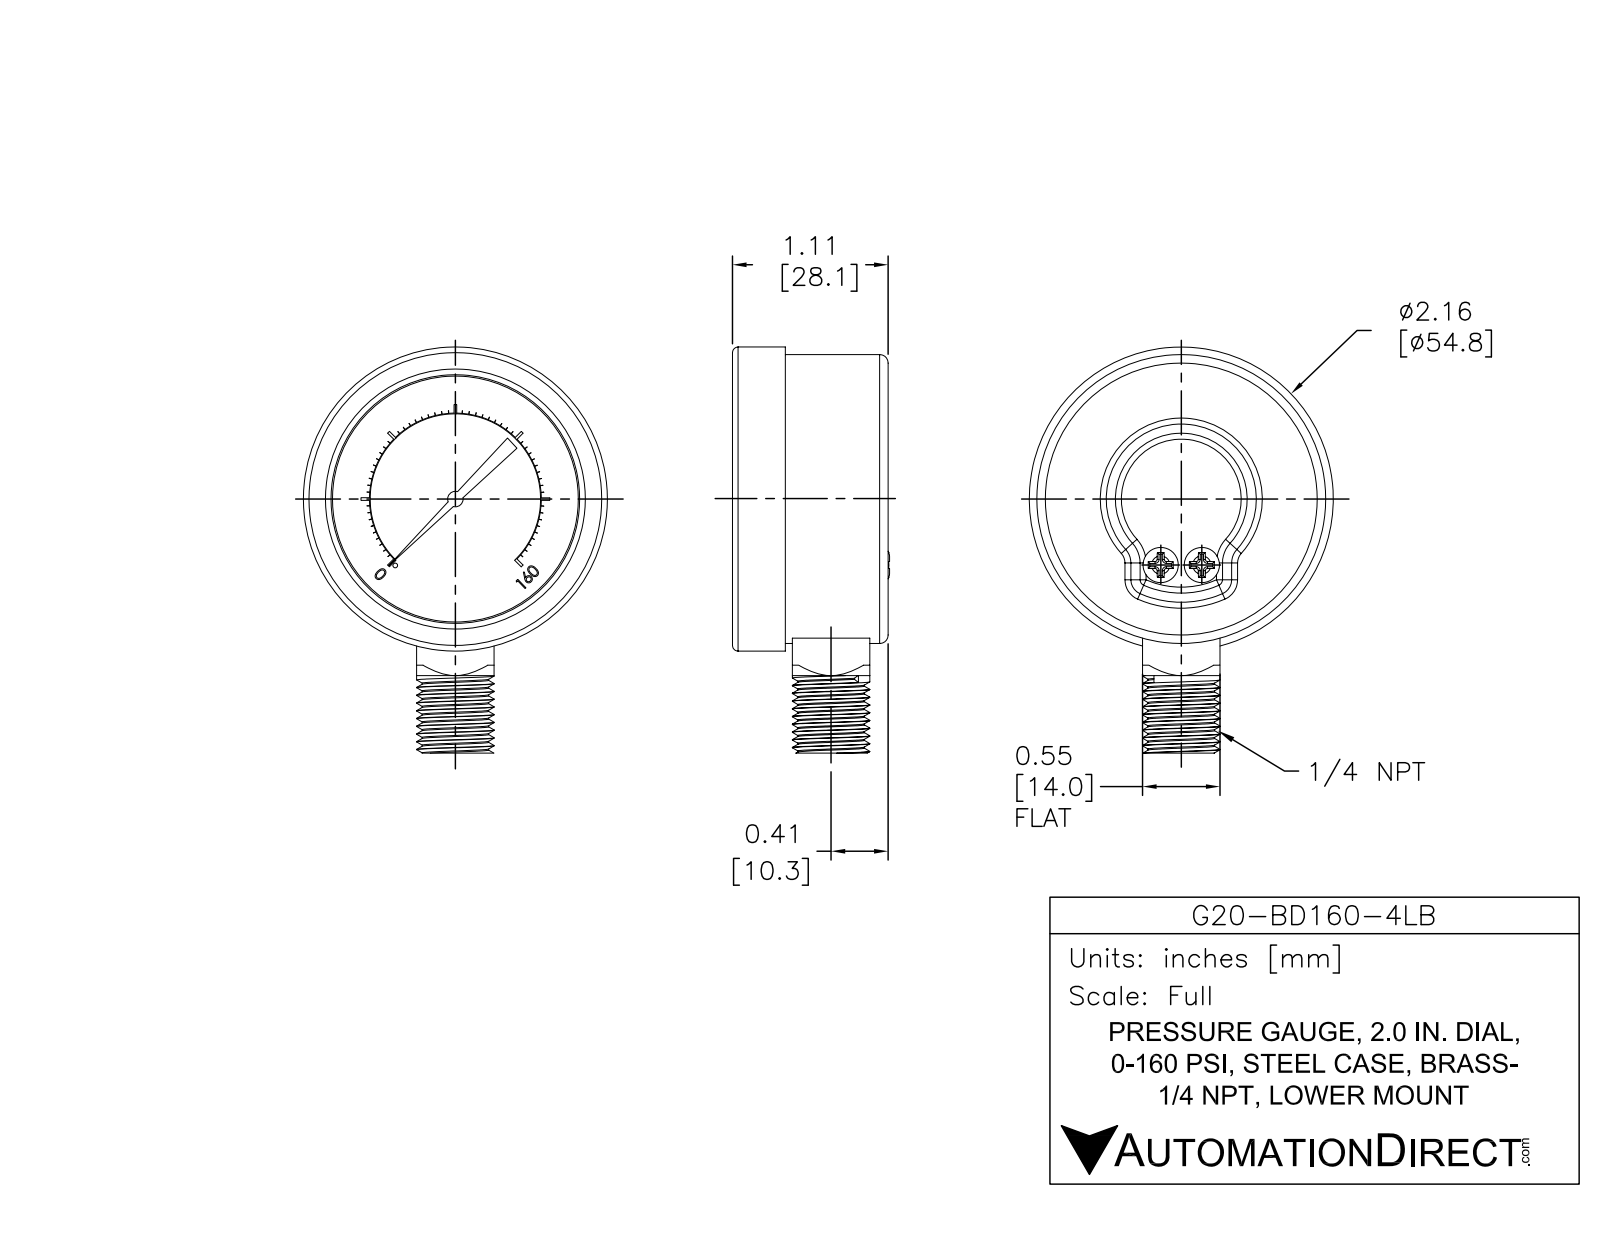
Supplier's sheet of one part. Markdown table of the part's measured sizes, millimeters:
| quantity | value |
| --- | --- |
| part name | G20-BD160-4LB |
| STEP written by | SolidWorks 2021 (AUTOMOTIVE_DESIGN) |
| units | millimeters |
| bodies | 1 solid, 423 faces (277 planar, 81 cylindrical, 65 other) |
| overall size | 73.2 × 54.8 × 28.3 |
| volume | 52 140 mm³ |
| surface area | 11 630 mm² |
| round holes (diameter × count) | 3.6 × 1, 44.3 × 1 |
| round bosses / shafts (diameter × count) | 6.4 × 2, 54.8 × 1, 52.1 × 1, 14 × 1, 2.8 × 1, 0.8 × 1 |
| partial cylindrical surfaces (radius × count) | 1.5 × 4, 15.4 × 1, 15.5 × 1 |
| main face-to-face distances | 20.7, 28.1, 7.4, 2.5, 18.2, 25.5, 16, 18.5, 2.2, 9.5 |
